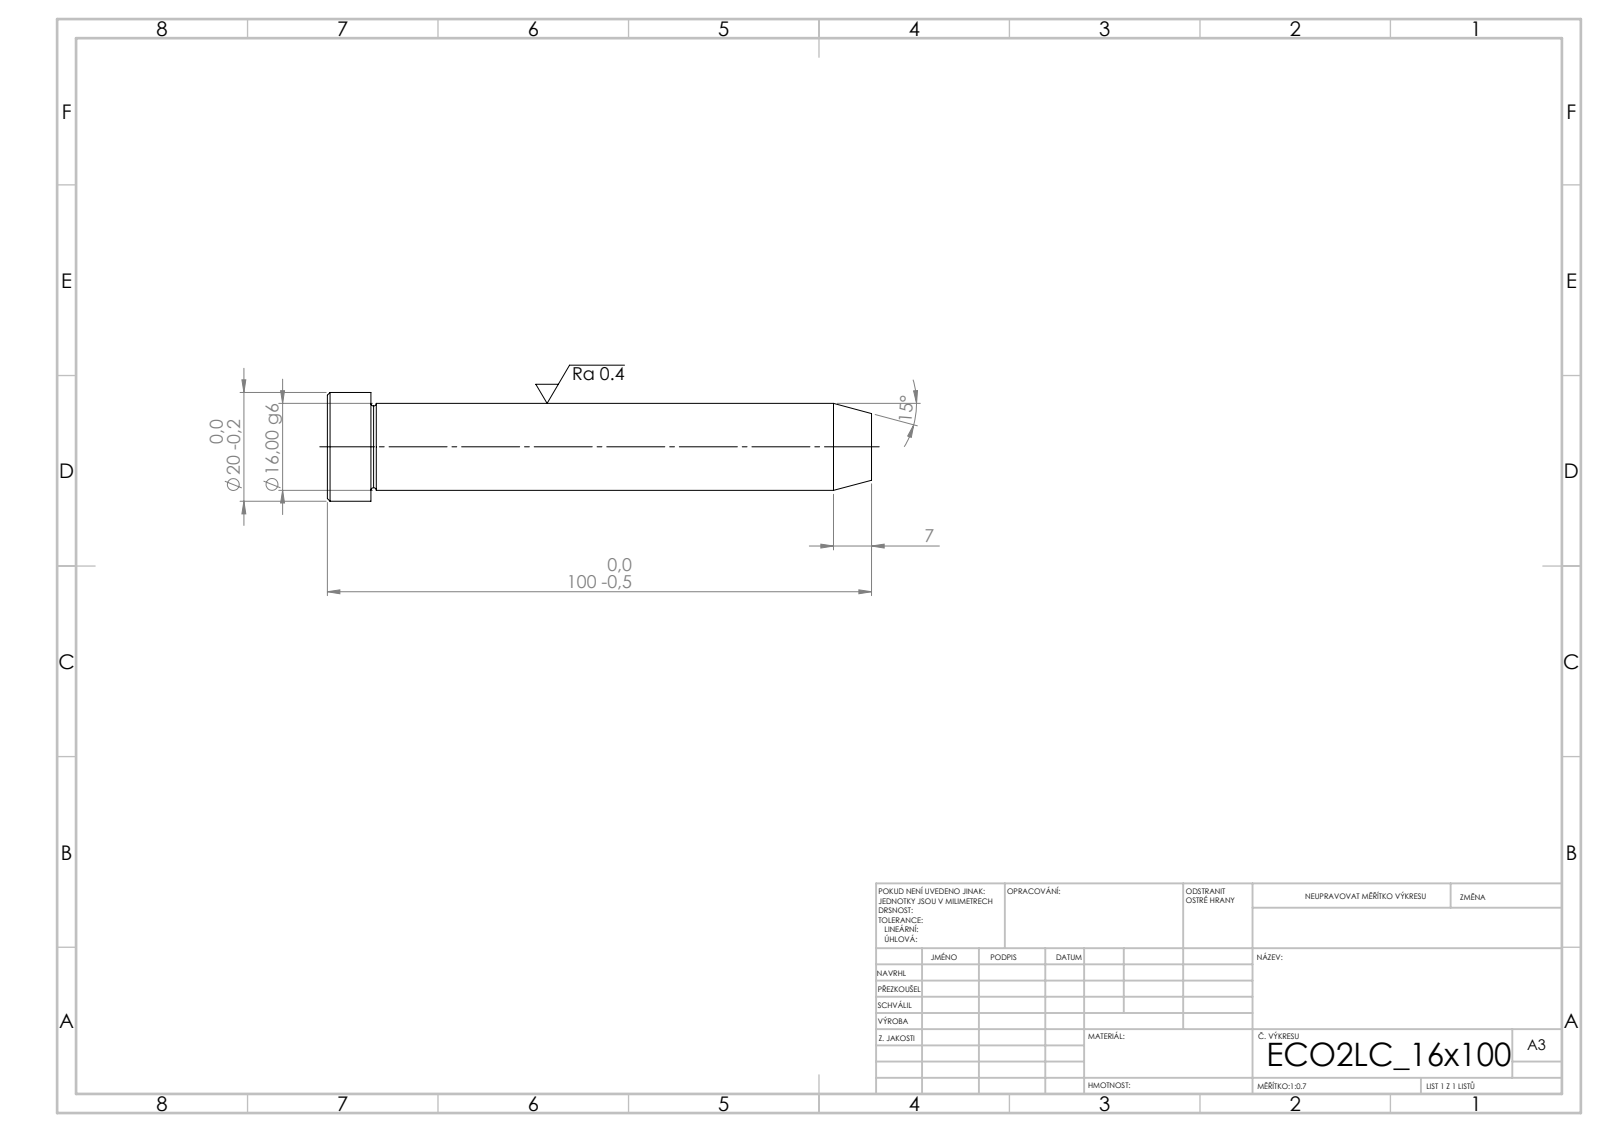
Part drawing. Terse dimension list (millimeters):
written by: SolidWorks 2019 (CONFIG_CONTROL_DESIGN)
unit: mm
bodies: 1 solid, 15 faces (3 planar, 4 cylindrical, 8 other)
size: 100 × 20 × 20
volume: 20 680 mm³; area: 5 649 mm²
bosses: 1× ⌀20, 1× ⌀16
face distances: 100, 92, 8
